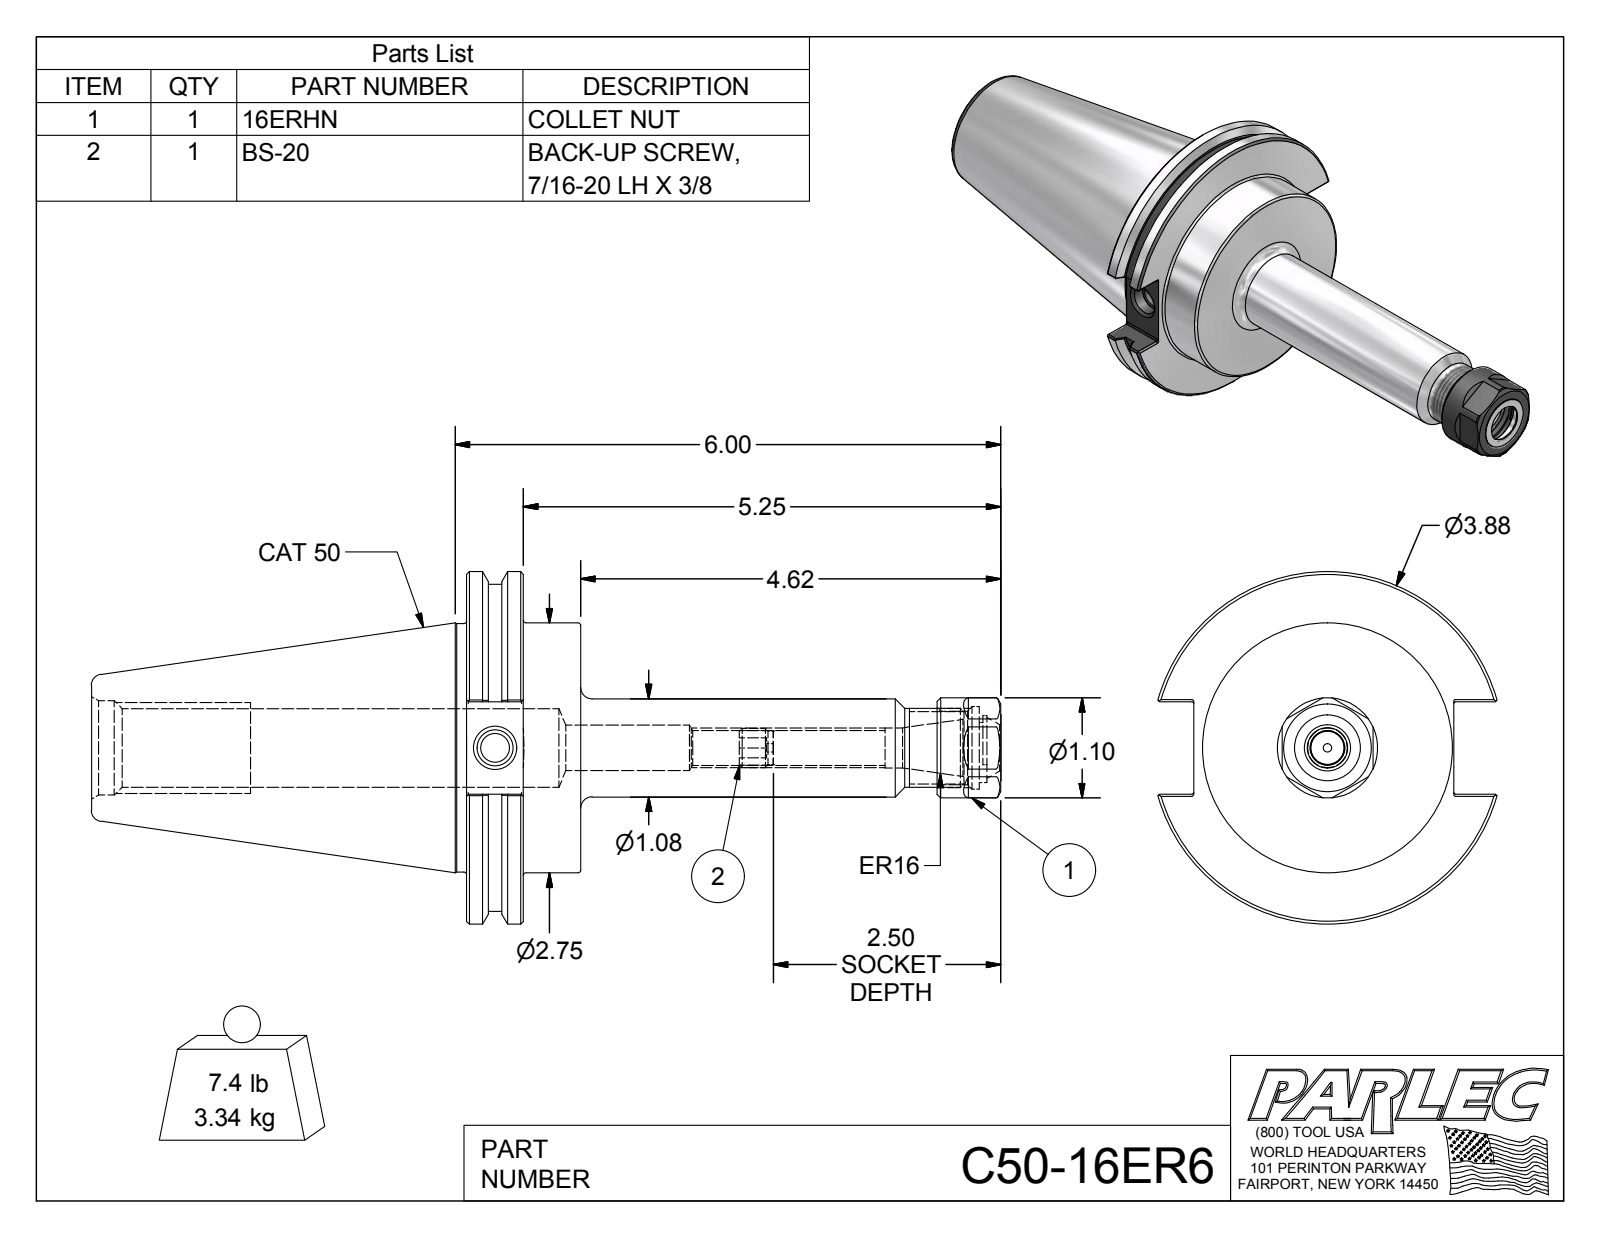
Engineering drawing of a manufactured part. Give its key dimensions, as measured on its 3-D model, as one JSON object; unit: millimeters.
{"part_name": "C50-16ER6; C50-16ER6-1; 16ERHN; BS-20", "step_written_by": "Autodesk Inventor 2012 (AUTOMOTIVE_DESIGN)", "units": "millimeters", "bodies": {"solids": 3, "faces": 146, "planar": 60, "cylindrical": 39, "other": 47}, "overall_size": [254.1, 98.4, 94.7], "volume_mm3": 428400, "surface_area_mm2": 65290, "round_holes": [[2.3, 1], [8, 1], [9.7, 1], [10.1, 1], [11.2, 1], [12.7, 1], [12.9, 1], [16.8, 1], [20.5, 1], [22, 1], [23, 1], [26.4, 1]], "round_bosses_or_shafts": [[98.4, 1], [91.3, 1], [69.9, 1], [69.3, 1], [28, 1], [27.4, 1], [22, 1], [18.4, 1]], "partial_cylinders_radius": [[0.5, 12], [9, 1]], "face_to_face_distances": [31.9, 15.9, 16, 133.4, 6, 104.8, 120.7, 136.7, 25.4, 72.6], "hole_center_spacings": [1.3]}
